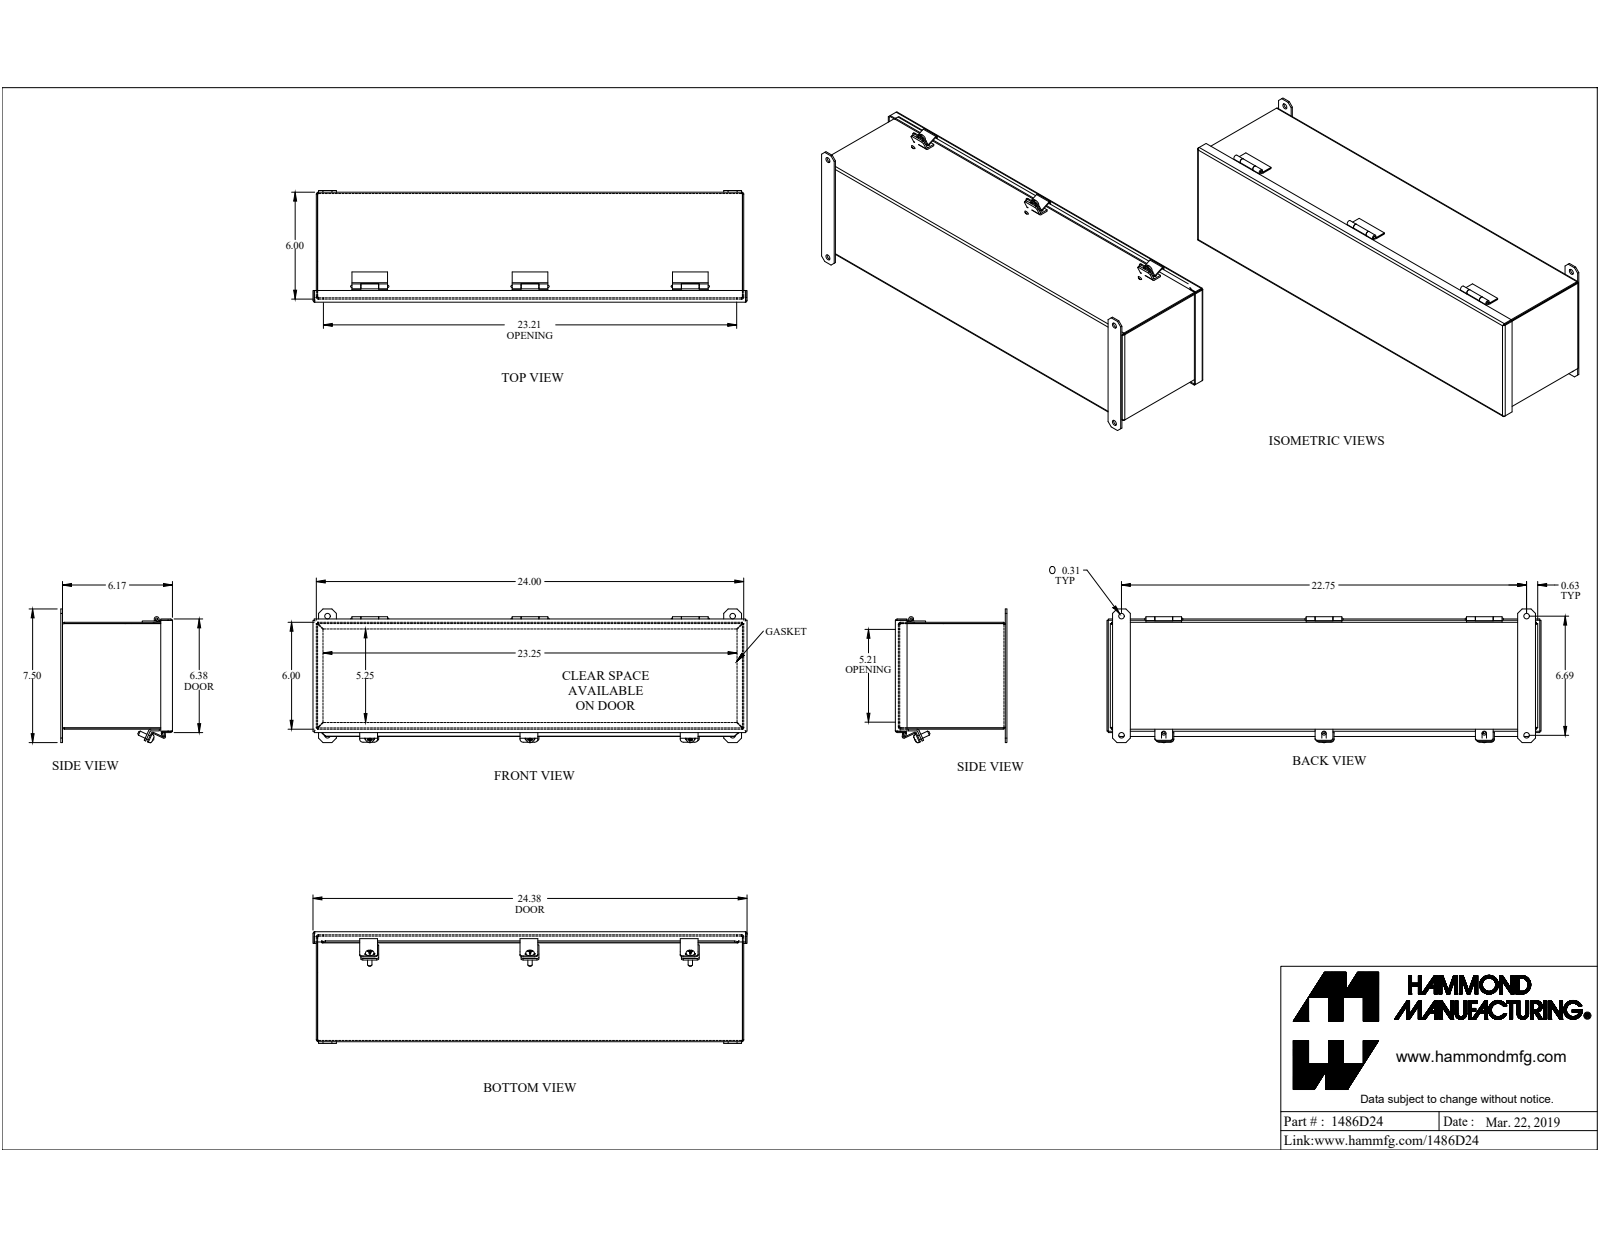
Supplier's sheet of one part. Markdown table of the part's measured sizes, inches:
| quantity | value |
| --- | --- |
| part name | 1486D24 |
| STEP written by | SolidWorks 2019 (CONFIG_CONTROL_DESIGN) |
| units | inches |
| bodies | 26 solids, 536 faces (355 planar, 124 cylindrical, 57 other) |
| overall size | 24.375 × 7.506 × 6.267 |
| volume | 61.83 in³ |
| surface area | 1 611 in² |
| round holes (diameter × count) | 0.313 × 4, 0.213 × 3, 0.125 × 1 |
| round bosses / shafts (diameter × count) | 0.48 × 3, 0.246 × 3, 0.275 × 1, 0.125 × 1 |
| partial cylindrical surfaces (radius × count) | 0.036 × 13, 0.108 × 13, 0.188 × 12, 0.25 × 12, 0.01 × 6, 0.141 × 6, 0.029 × 2, 0.086 × 2 |
| main face-to-face distances | 0.072, 5.928, 6.1, 6, 5.856, 6.172, 6.028, 23.928, 0.187, 0.259 |
| hole center spacings | 6.688, 9, 22.75, 23.713, 18 |
